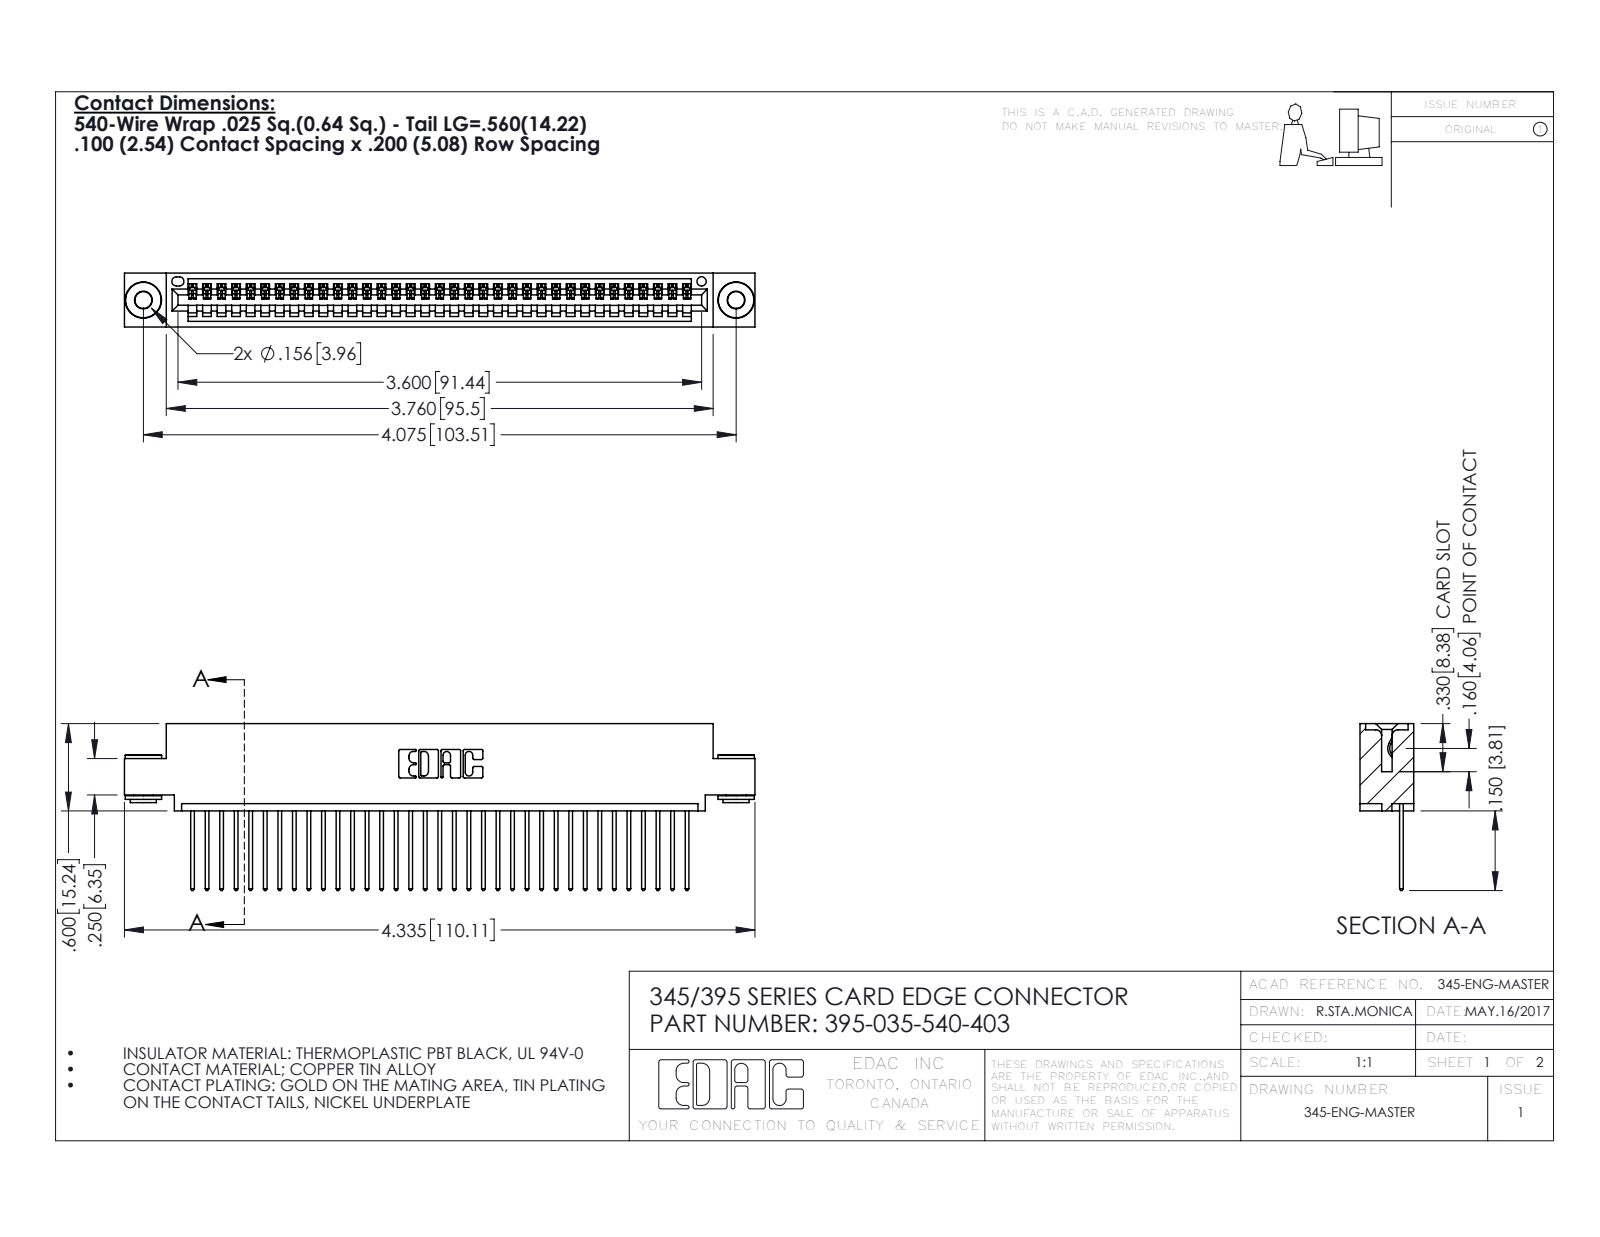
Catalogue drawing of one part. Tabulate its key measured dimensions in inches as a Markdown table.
| quantity | value |
| --- | --- |
| part name | 345-250-002_345-250-002-102; 345-292-001_345-293-140; 345 Part_0.110 Offset - 0.156 Dia-TH; 395-035-540-403 |
| STEP written by | SolidWorks 2016 (CONFIG_CONTROL_DESIGN) |
| units | inches |
| bodies | 38 solids, 2198 faces (1494 planar, 696 cylindrical, 8 other) |
| overall size | 4.335 × 1.147 × 0.37 |
| volume | 0.634 in³ |
| surface area | 22.25 in² |
| round holes (diameter × count) | 0.116 × 2, 0.156 × 2, 0.064 × 1 |
| round bosses / shafts (diameter × count) | 0.25 × 2, 0.18 × 2, 0.136 × 2 |
| partial cylindrical surfaces (radius × count) | 0.006 × 70, 0.01 × 70, 0.01 × 22, 0.007 × 6, 0.031 × 6, 0.026 × 3, 0.031 × 2, 0.04 × 2 |
| main face-to-face distances | 0.072, 0.298, 0.37, 0.025, 0.098, 0.272, 0.2, 0.225, 0.149, 0.072 |
| hole center spacings | 0.27, 3.839, 4.075 |
